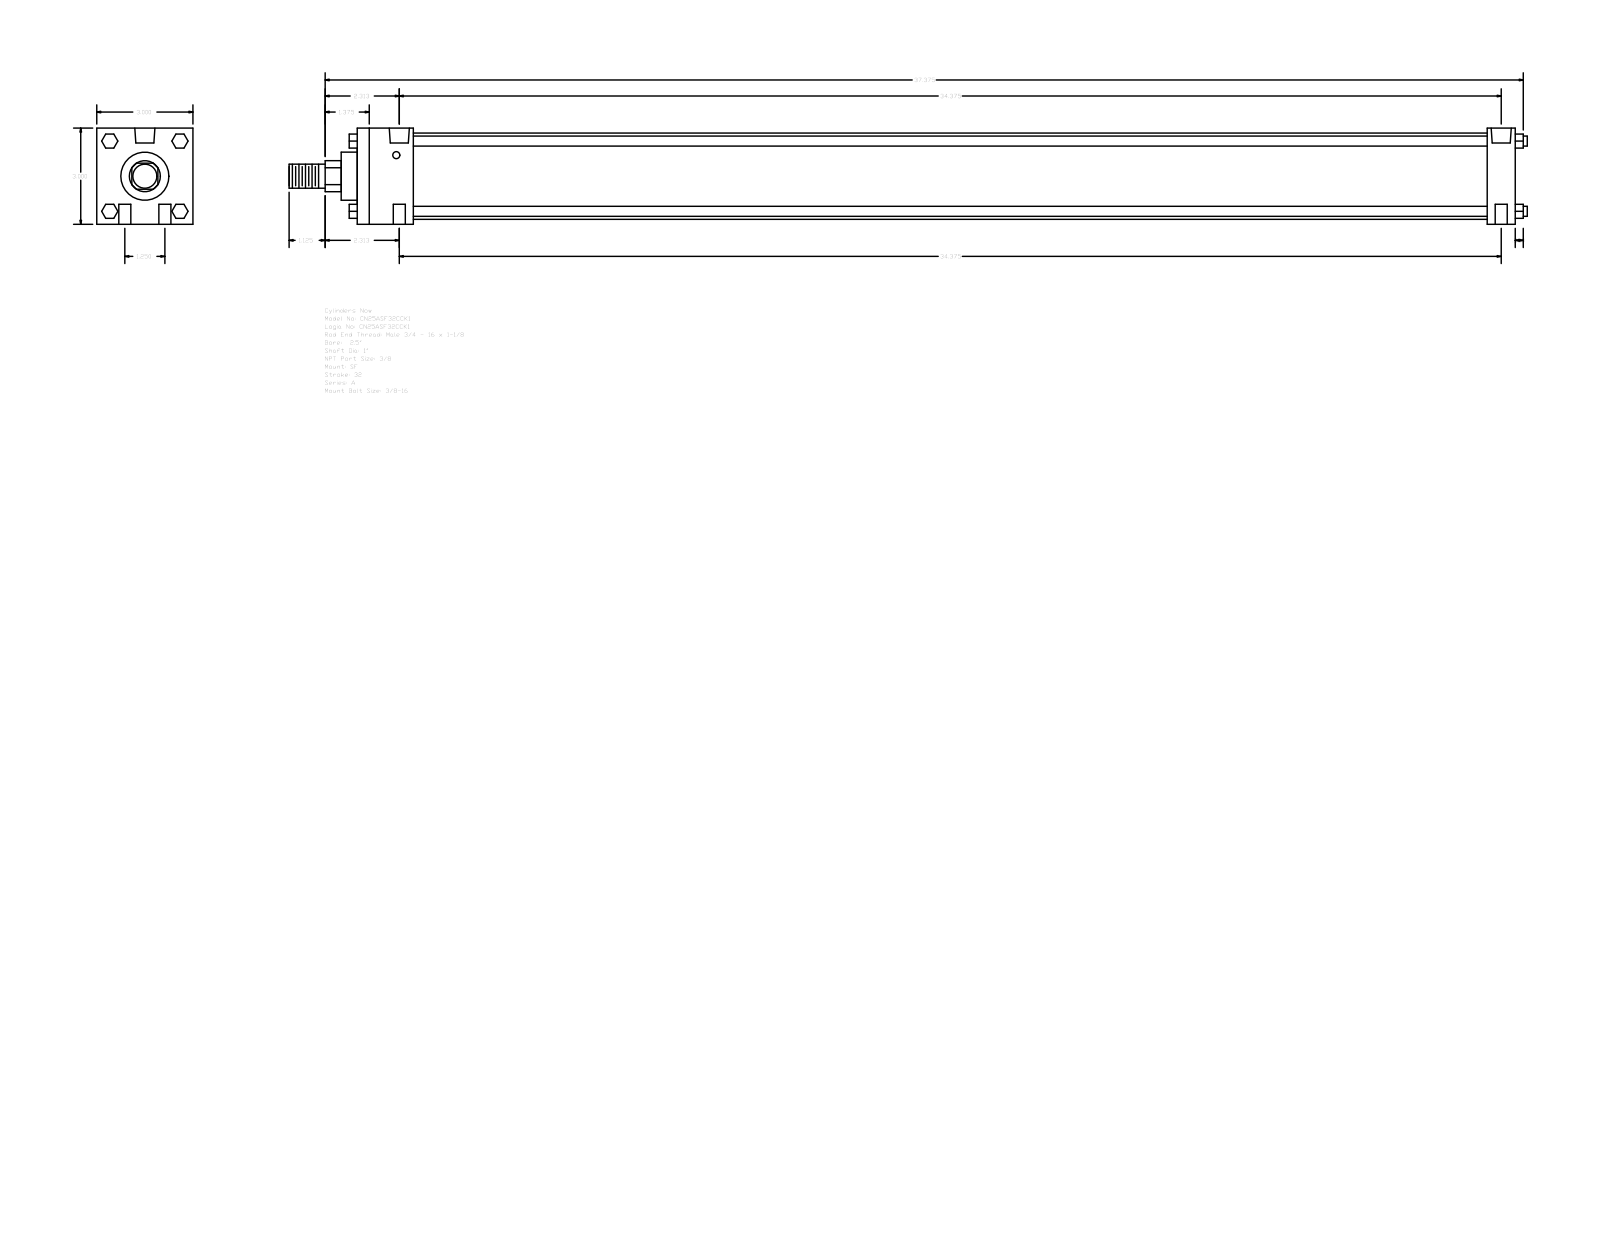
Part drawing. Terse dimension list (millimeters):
name: A_SF__0250_1
written by: GSSL Pune (CONFIG_CONTROL_DESIGN)
unit: mm
bodies: 0 solids, 124 faces (94 planar, 30 cylindrical, 0 other)
size: 981.08 × 76.2 × 76.2
holes: 4× ⌀9.53, 2× ⌀5.56, 2× ⌀15.93
bosses: 4× ⌀7.94, 1× ⌀68.33, 1× ⌀38.1, 1× ⌀25.4, 1× ⌀19.05
rounds: 1× R12.29
face distances: 76.2, 917.58, 895.35, 22.23, 44.45, 850.9, 873.13, 12.7, 930.28, 6.35
hole spacings: 15.88, 873.26, 873.12, 31.76, 873.7, 877.88
